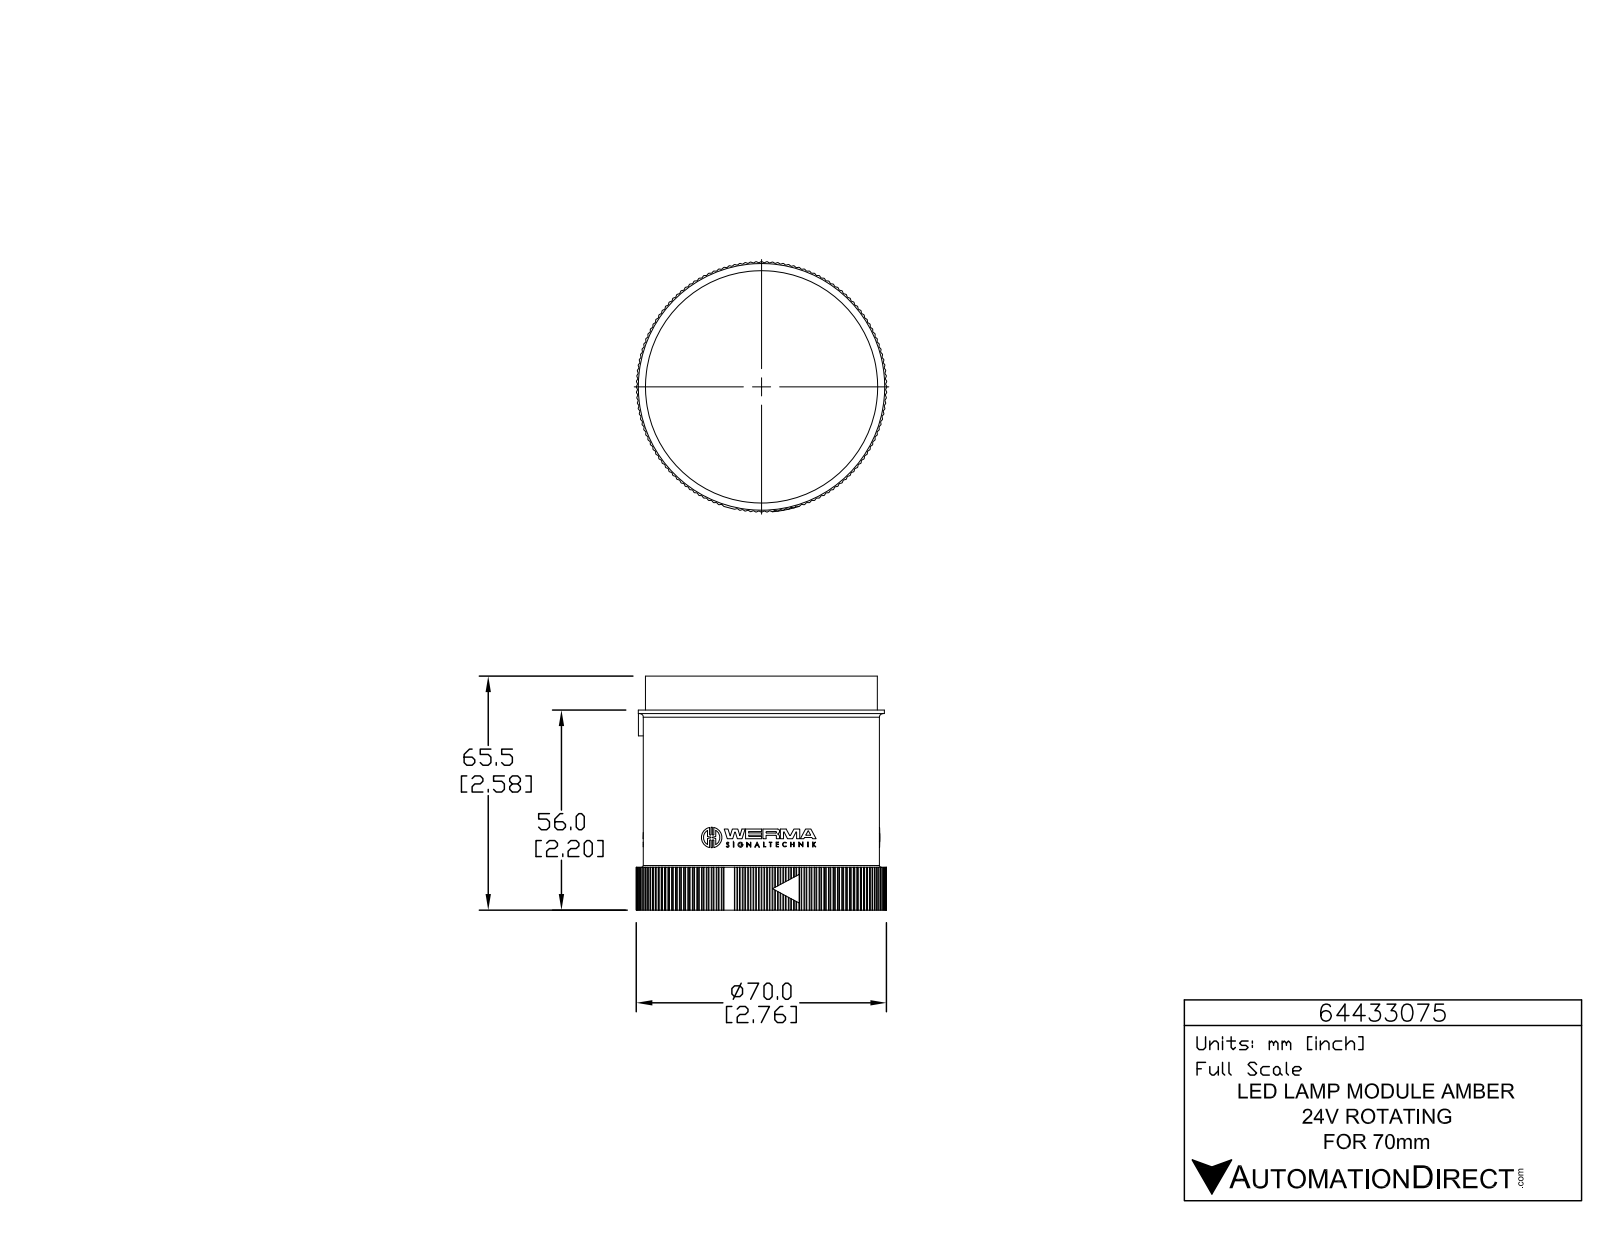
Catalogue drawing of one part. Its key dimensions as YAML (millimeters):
part_name: "64433075"
step_written_by: "SolidWorks 2015 (AUTOMOTIVE_DESIGN)"
units: millimeters
bodies: {solids: 1, faces: 1400, planar: 832, cylindrical: 563, other: 5}
overall_size: [70.2, 70.2, 65.5]
volume: 197000
surface_area: 24180
round_holes:
  - {diameter: 1, count: 3}
  - {diameter: 65.4, count: 1}
round_bosses_or_shafts:
  - {diameter: 5.7, count: 3}
  - {diameter: 1.4, count: 3}
  - {diameter: 69, count: 1}
  - {diameter: 66.2, count: 1}
  - {diameter: 65, count: 1}
partial_cylinders:
  - {radius: 0.2, count: 285}
  - {radius: 0.2, count: 6}
  - {radius: 0.2, count: 6}
  - {radius: 0.2, count: 6}
  - {radius: 3.3, count: 6}
  - {radius: 0.1, count: 3}
  - {radius: 0.1, count: 3}
  - {radius: 0.2, count: 3}
face_to_face_distances: [55.9, 62.3, 9.6, 65.5, 56, 46.4, 9.5, 62.3, 12, 2.4]
